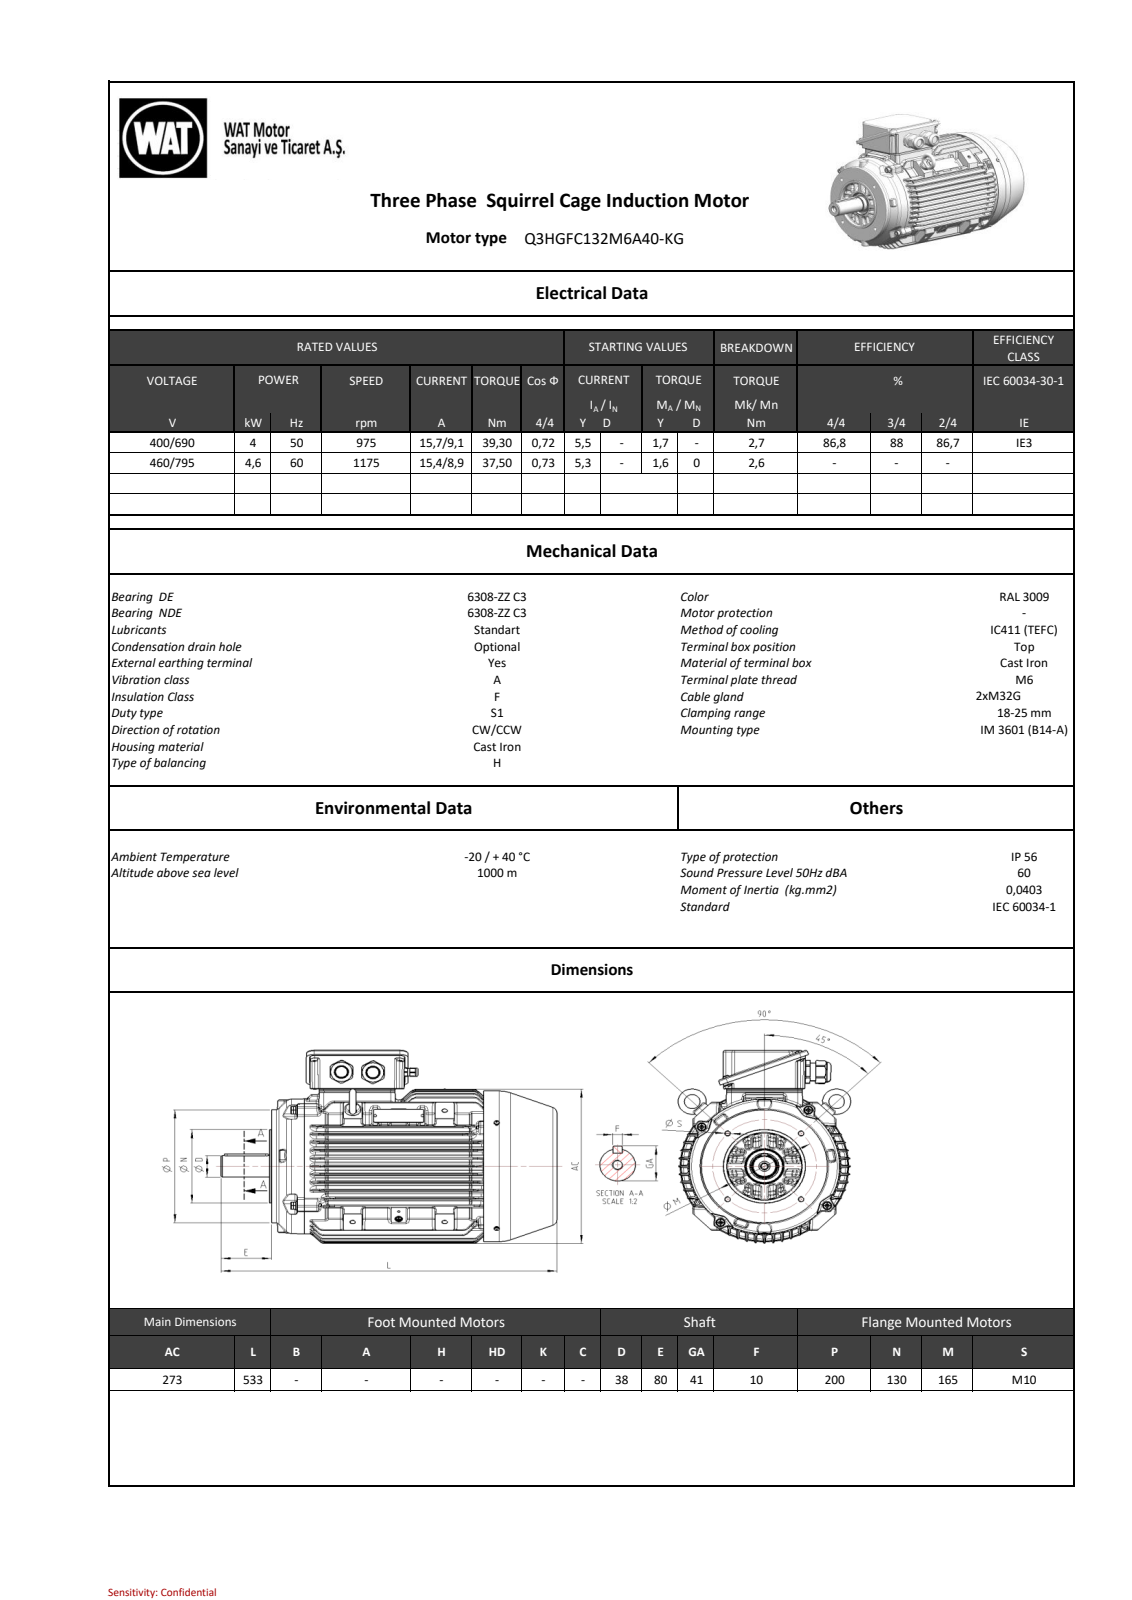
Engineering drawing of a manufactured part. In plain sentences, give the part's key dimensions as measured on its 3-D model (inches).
The part is named "260021E4F5C7p849". Its 3-D file was written by "SIEMENS PLM Software NX 11.0 (AUTOMOTIVE_DESIGN)". It is 0 solids with 4910 faces: 982 planar, 1341 cylindrical and 2587 other. Overall it measures 20.984 by 13.463 by 10.791 inches. Round holes: 10 of diameter 0.335, 8 of diameter 0.217, 8 of diameter 0.268, 5 of diameter 0.165, 2 of diameter 0.098, 2 of diameter 0.394, 2 of diameter 0.748, 2 of diameter 0.827, 1 of diameter 0.406, 1 of diameter 0.512, 1 of diameter 1.346, 1 of diameter 2.299. Round bosses or shafts: 4 of diameter 0.512, 4 of diameter 0.341, 4 of diameter 0.315, 3 of diameter 0.583, 2 of diameter 1.417, 2 of diameter 1.358, 2 of diameter 1.23, 2 of diameter 0.984. Partial cylindrical surfaces (rounded edges, fillets, slot ends): 235 of radius 0.157, 123 of radius 0.118, 106 of radius 0.059, 85 of radius 0.079, 52 of radius 0.071, 35 of radius 0.039, 24 of radius 1.024, 24 of radius 1.378. The main face-to-face distances are 0.542, 0.544, 1.086, 1.092, 1.633, 0.547, 2.202, 2.183, 1.641, 1.096. The hole center spacings are 5.354, 2.896, 1.682, 4.783, 5.295, 6.231, 6.765, 8.002.
